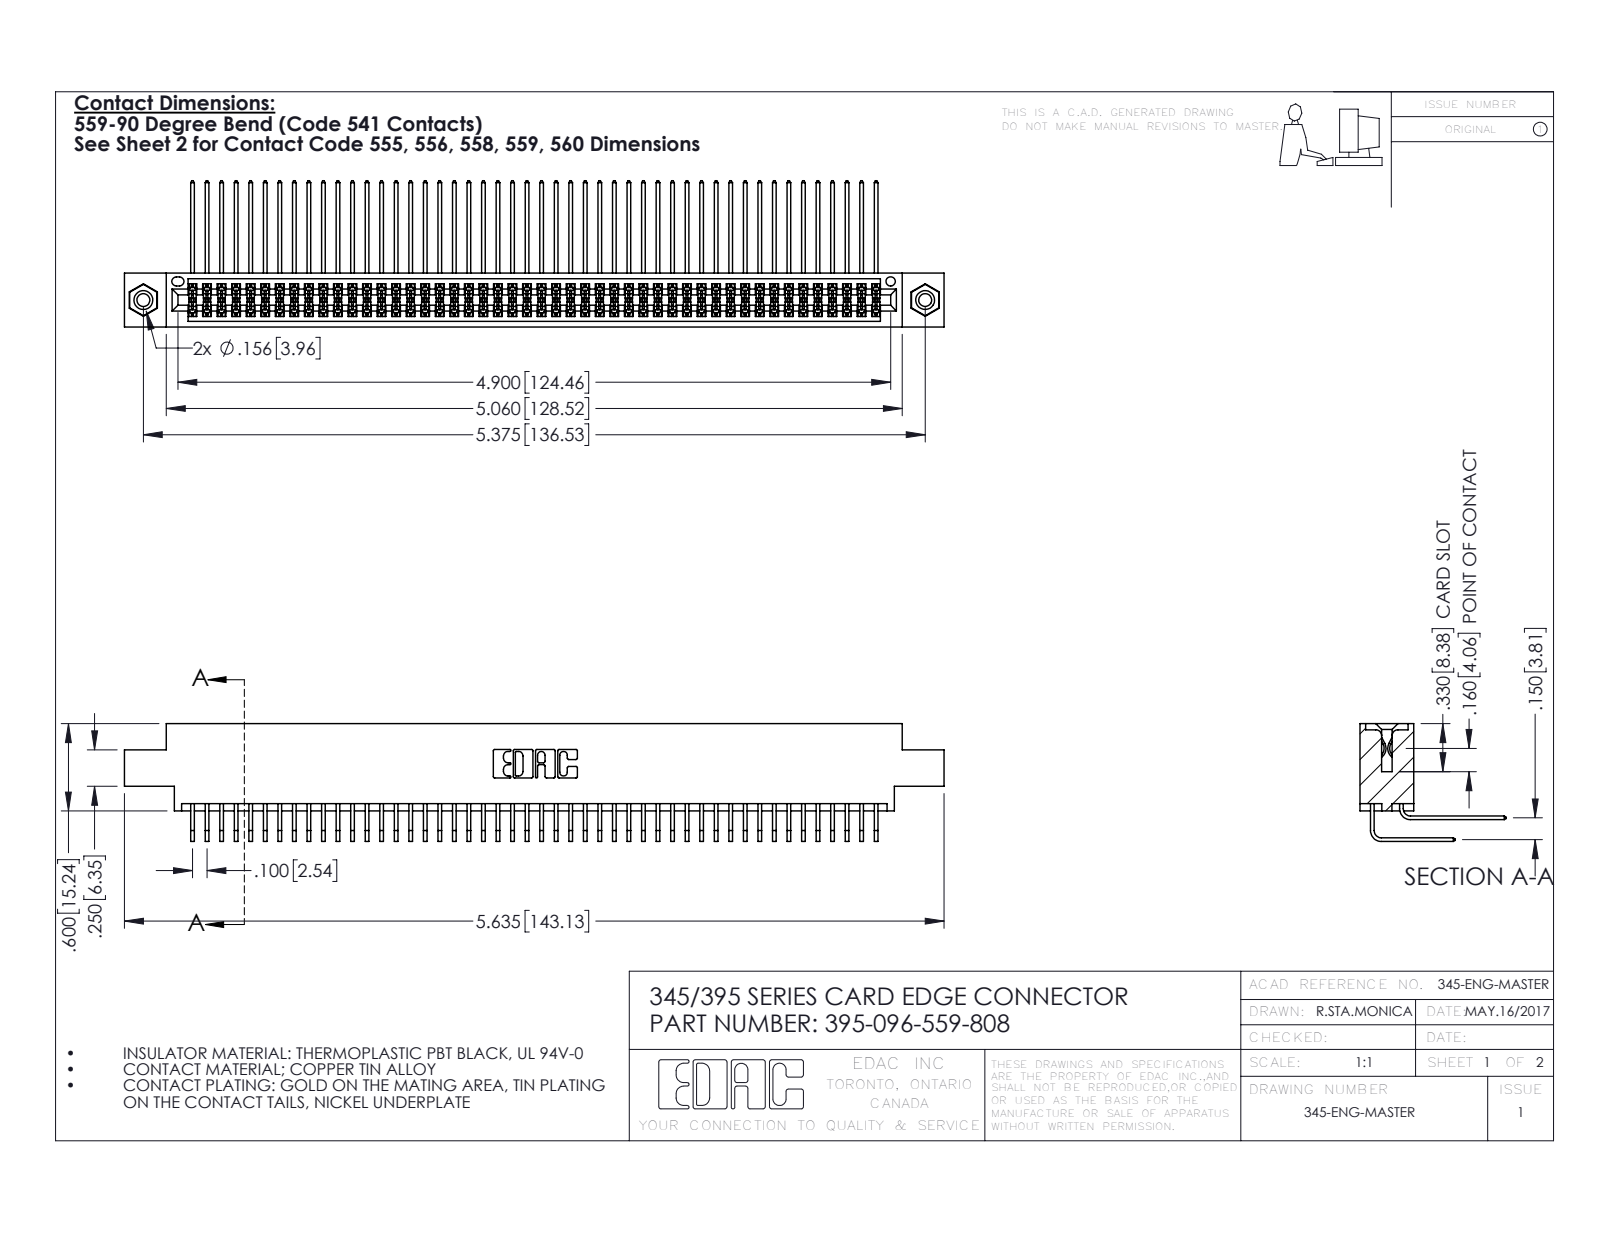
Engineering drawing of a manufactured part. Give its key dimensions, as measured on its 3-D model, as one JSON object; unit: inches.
{"part_name": "345 Part_0.170 Offset - 0.156 Dia-TI; 345-292-001_559 Tail - 2; 395-096-559-808; 345-250-001_345-250-003-102 (+1 more)", "step_written_by": "SolidWorks 2016 (CONFIG_CONTROL_DESIGN)", "units": "inches", "bodies": {"solids": 99, "faces": 5182, "planar": 3476, "cylindrical": 1690, "other": 16}, "overall_size": [5.635, 1.005, 0.809], "volume_in3": 0.878, "surface_area_in2": 37.44, "round_holes": [[0.089, 2], [0.125, 2], [0.156, 2], [0.064, 1]], "round_bosses_or_shafts": [[0.155, 2]], "partial_cylinders_radius": [[0.006, 145], [0.01, 22], [0.007, 6], [0.031, 6], [0.026, 3], [0.014, 2], [0.019, 2], [0.022, 2]], "face_to_face_distances": [0.072, 0.298, 0.37, 0.2, 0.098, 0.272, 0.025, 0.225, 0.175, 0.15], "hole_center_spacings": [0.27, 5.139, 5.375]}
